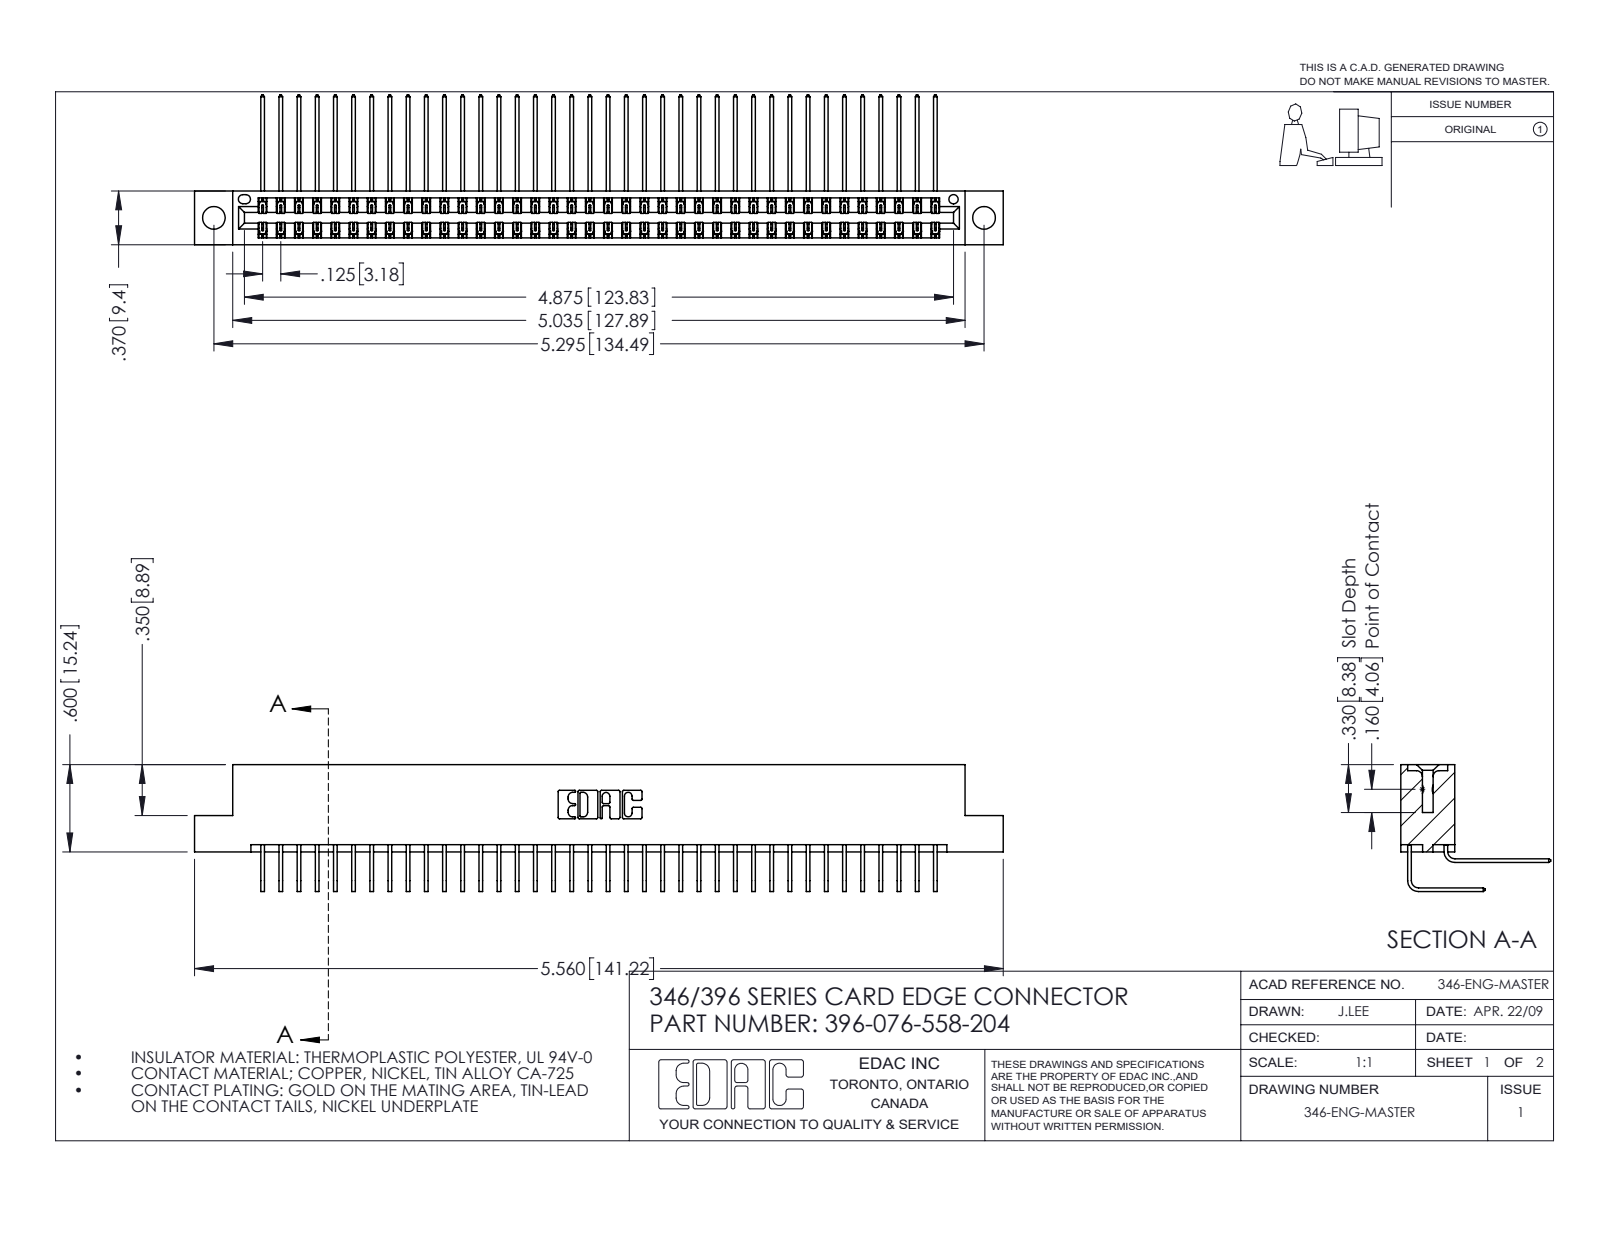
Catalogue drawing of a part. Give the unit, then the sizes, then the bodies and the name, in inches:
Units: inches
Overall size (bounding box): 5.56 × 1.03 × 0.873
Round holes (diameter × count): ⌀0.156 ×2, ⌀0.064 ×1
Partial cylindrical surfaces — rounded edges, fillets, slot ends (radius × count): R0.006 ×114, R0.01 ×22, R0.007 ×6, R0.031 ×6, R0.026 ×3, R0.014 ×2, R0.022 ×2, R0.024 ×2
Main face-to-face distances: 0.048, 0.322, 0.025, 0.37, 0.25, 0.072, 0.298, 0.275, 0.148, 0.222
Hole centre spacings: 0.246, 5.086, 5.295
Volume: 0.86 in³ · Surface area: 32.89 in²
Bodies: 77 solids, 4226 faces (2888 planar, 1338 cylindrical, 0 other)
Part name (STEP PRODUCT): 345-292-001_558 Tail - 2; 345-292-001_558 559 Tail - 1; 346 Part_Flush Mounting Lugs - 0.156 Dia-TH; 396-076-558-204
STEP written by: SolidWorks 2016 (CONFIG_CONTROL_DESIGN)
